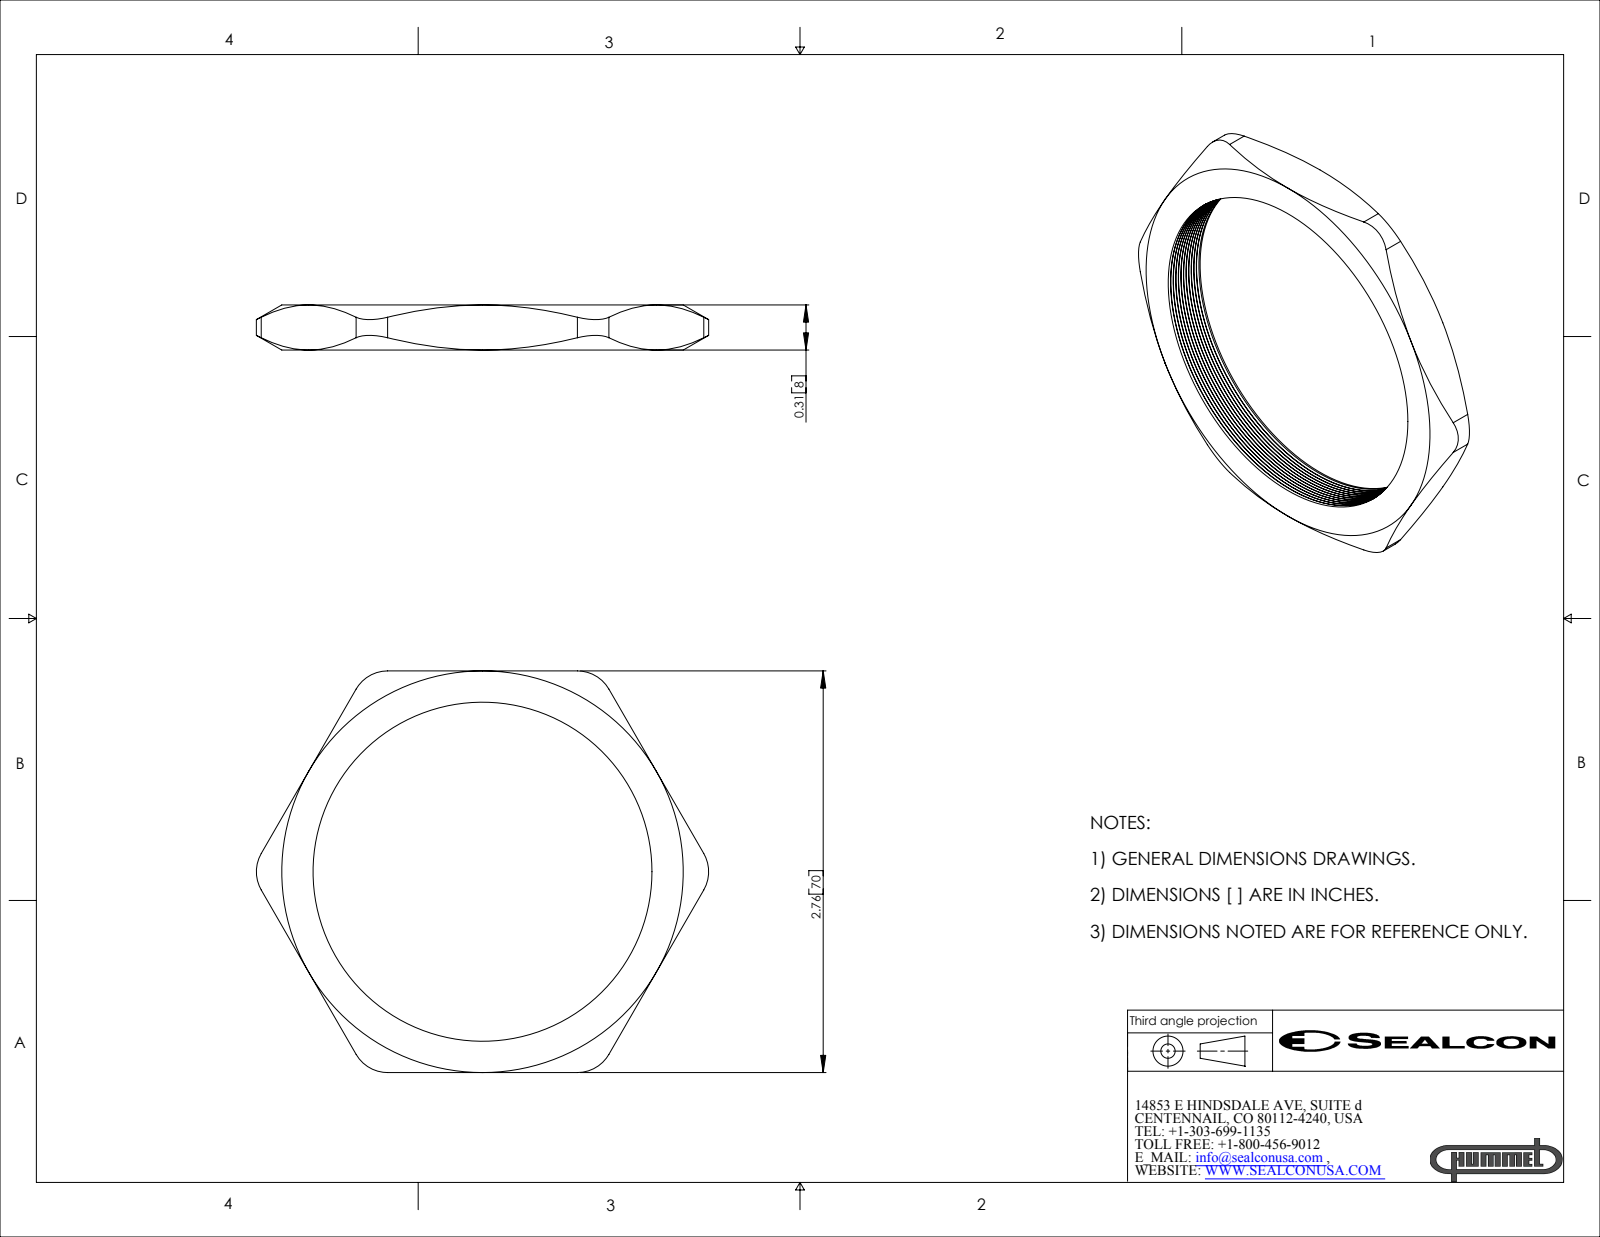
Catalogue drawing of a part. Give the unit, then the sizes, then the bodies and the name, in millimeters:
Units: millimetres
Overall size (bounding box): 79 × 70.1 × 7.9
Round holes (diameter × count): ⌀59.2 ×1
Partial cylindrical surfaces — rounded edges, fillets, slot ends (radius × count): R6.4 ×6
Main face-to-face distances: 7.9, 70.1
Volume: 10 700 mm³ · Surface area: 7 297 mm²
Bodies: 1 solid, 101 faces (8 planar, 31 cylindrical, 62 other)
Part name (STEP PRODUCT): NP-48-GY
STEP written by: SolidWorks 2007 (CONFIG_CONTROL_DESIGN)
